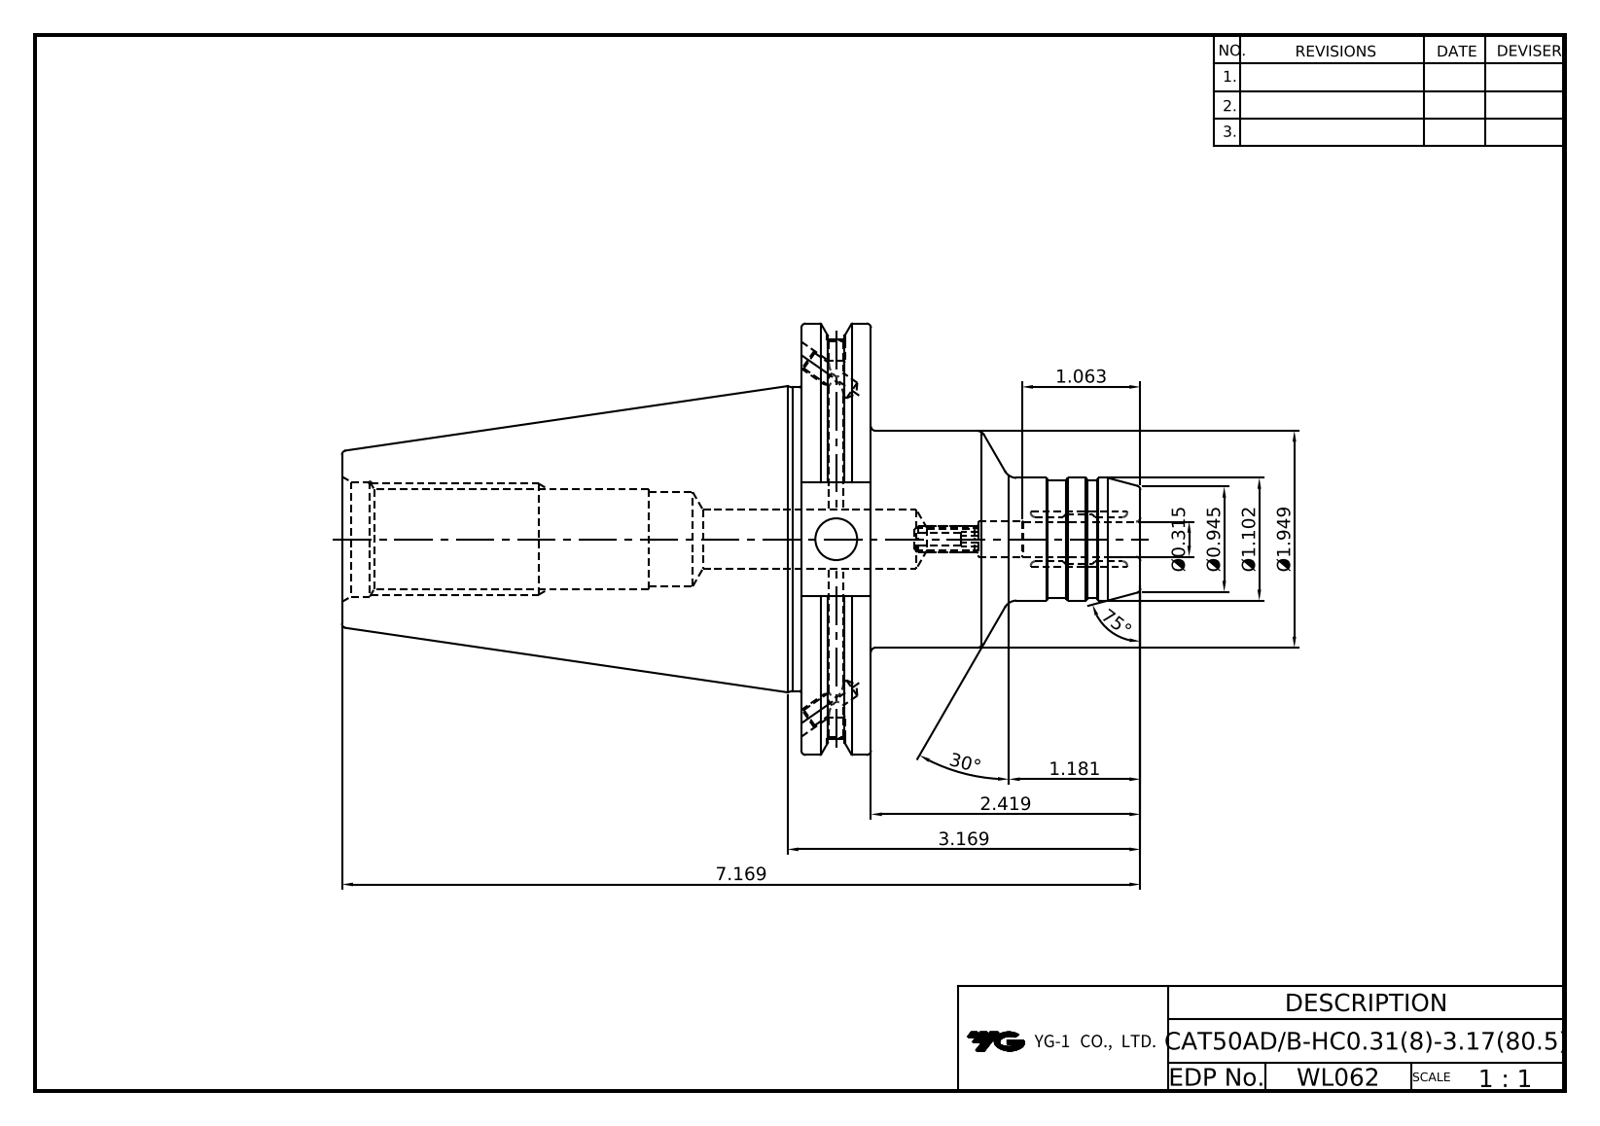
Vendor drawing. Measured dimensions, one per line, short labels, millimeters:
name: LO-CAT50ADB-HC8-80.5
written by: Autodesk Inventor 2022 (AUTOMOTIVE_DESIGN)
unit: mm
bodies: 1 solid, 108 faces (37 planar, 33 cylindrical, 38 other)
size: 182.1 × 98.42 × 94.69
volume: 397 588 mm³; area: 52 358 mm²
holes: 2× ⌀3.24, 2× ⌀4.13, 2× ⌀4.2, 2× ⌀5, 1× ⌀4.92, 1× ⌀8, 1× ⌀8.6, 1× ⌀9.53, 1× ⌀13.5, 1× ⌀20.5, 1× ⌀21.97, 1× ⌀26.2
bosses: 1× ⌀98.42, 1× ⌀91.29, 1× ⌀69.25, 1× ⌀49.5, 1× ⌀28, 1× ⌀27
face distances: 15.88, 104.77, 120.65, 182.1, 77.33, 61.45, 73.03, 25.9, 110.82, 6.05
